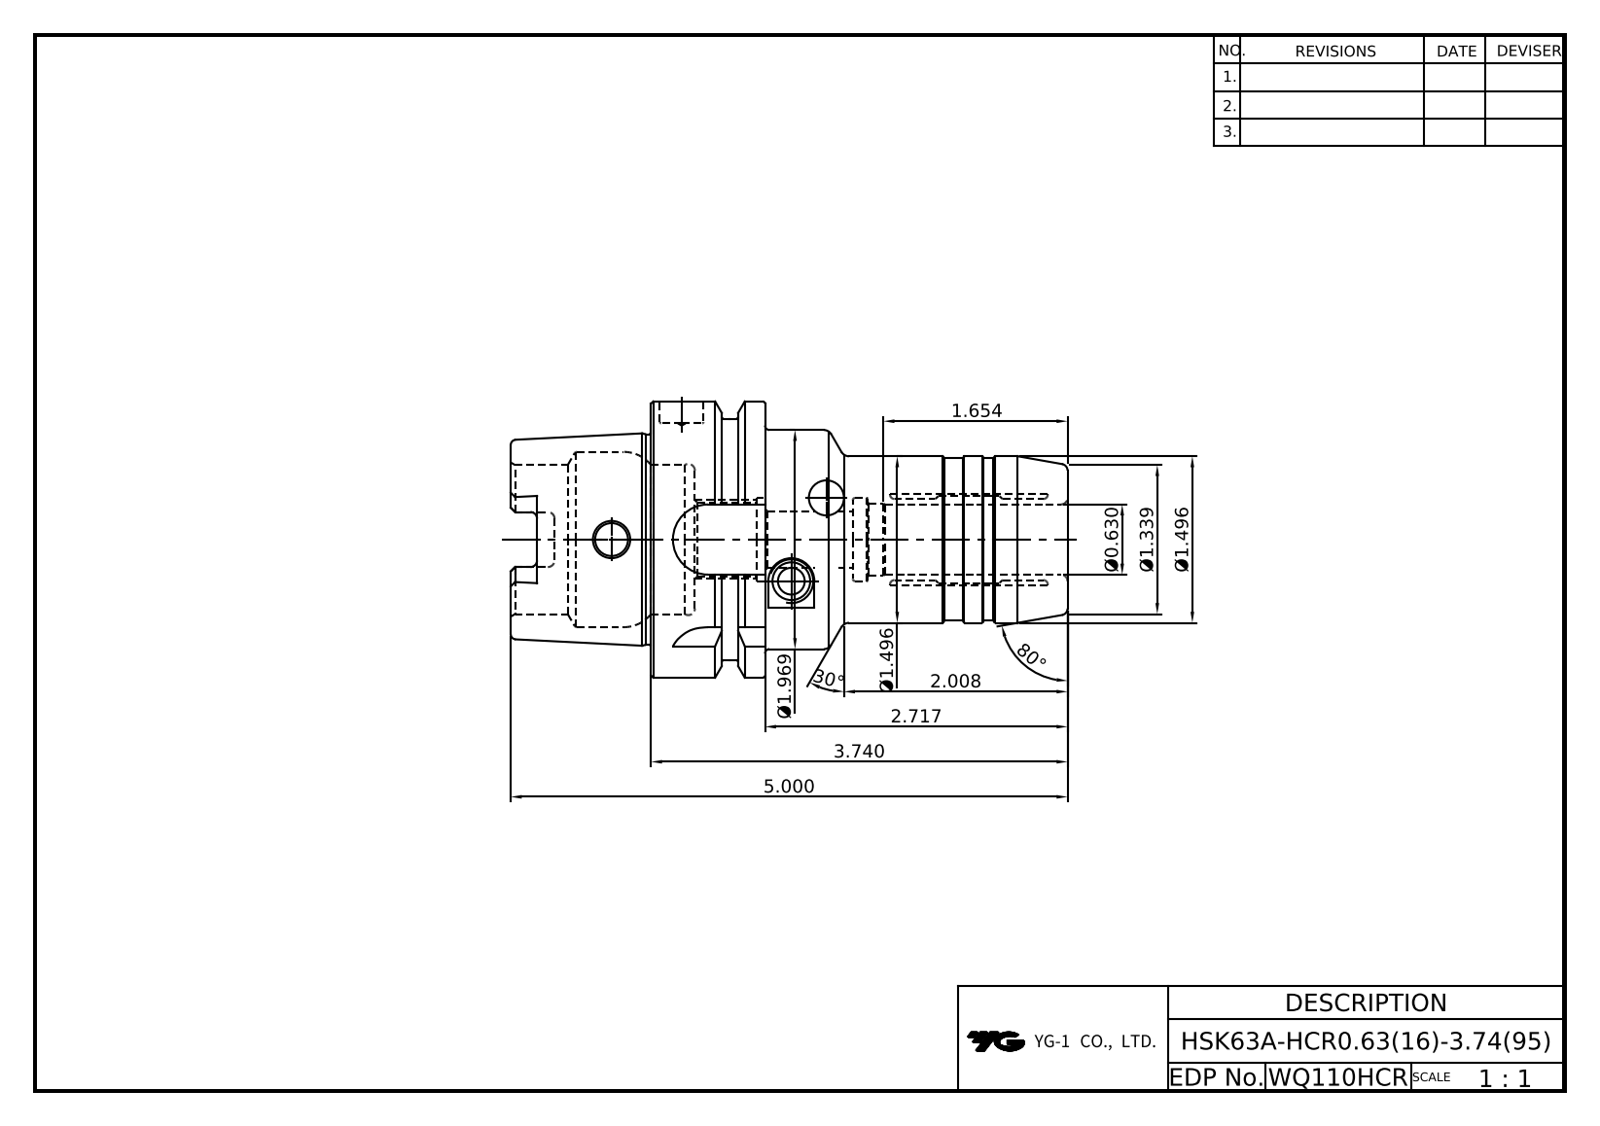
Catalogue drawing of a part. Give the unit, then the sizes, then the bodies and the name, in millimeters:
Units: millimetres
Overall size (bounding box): 127 × 63 × 63
Round holes (diameter × count): ⌀7.5 ×1, ⌀10 ×1, ⌀13.2 ×1, ⌀16 ×1, ⌀16.92 ×1, ⌀19 ×1, ⌀34 ×1, ⌀40 ×1
Round bosses / shafts (diameter × count): ⌀63 ×1, ⌀55 ×1, ⌀50 ×1, ⌀48.04 ×1, ⌀38 ×1, ⌀37 ×1
Partial cylindrical surfaces — rounded edges, fillets, slot ends (radius × count): R1.5 ×6, R2.88 ×4, R8 ×4
Main face-to-face distances: 26, 69, 10, 95, 16, 85, 32, 42, 58, 127
Volume: 158 435 mm³ · Surface area: 33 625 mm²
Bodies: 1 solid, 134 faces (41 planar, 37 cylindrical, 56 other)
Part name (STEP PRODUCT): LO-HSK63A-HCR16-95
STEP written by: Autodesk Inventor 2020 (AUTOMOTIVE_DESIGN)
